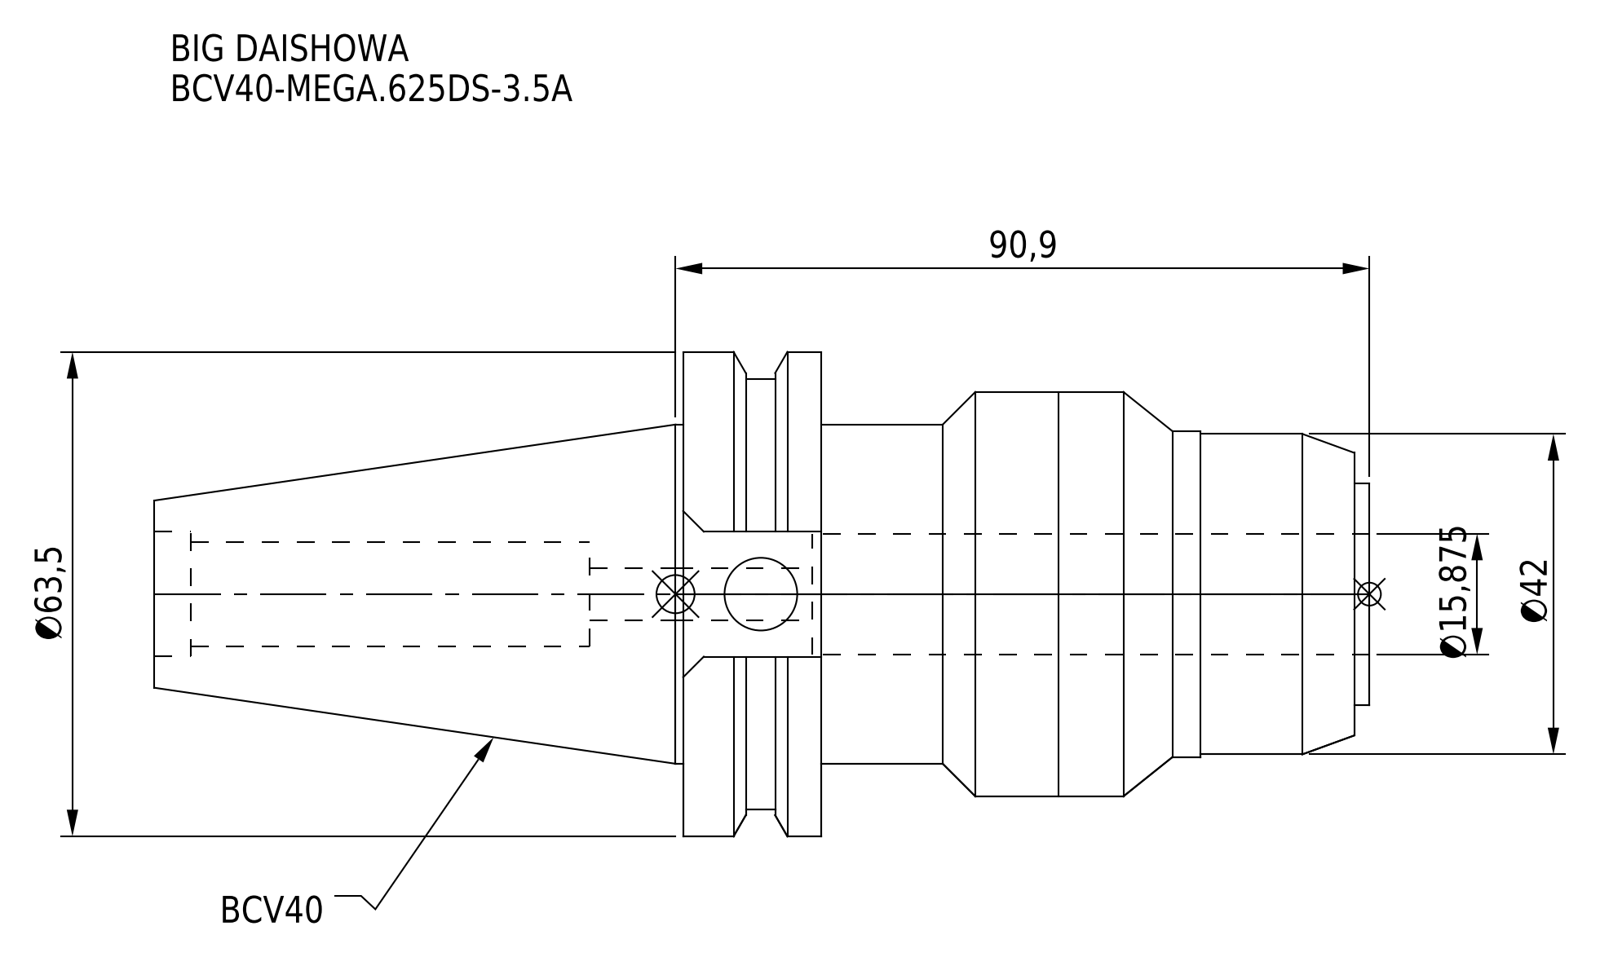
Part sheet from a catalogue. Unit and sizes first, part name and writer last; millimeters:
Units: millimetres
Overall size (bounding box): 159.15 × 63.5 × 61.35
Round holes (diameter × count): ⌀6.8 ×1, ⌀9.53 ×1, ⌀13.6 ×1, ⌀15.88 ×1, ⌀16.32 ×1
Round bosses / shafts (diameter × count): ⌀63.5 ×1, ⌀56.36 ×1, ⌀53 ×1, ⌀44.45 ×1, ⌀42.7 ×1, ⌀42 ×1, ⌀29 ×1
Main face-to-face distances: 18.05, 71.85, 89.9, 2, 69.85, 87.9, 159.15, 157.15, 87.3, 69.25
Volume: 213 248 mm³ · Surface area: 34 167 mm²
Bodies: 1 solid, 66 faces (24 planar, 30 cylindrical, 12 other)
Part name (STEP PRODUCT): BCV40-MEGA_625DS-3_5A
STEP written by: CREO PARAMETRIC BY PTC INC, 2016380 (AUTOMOTIVE_DESIGN)
